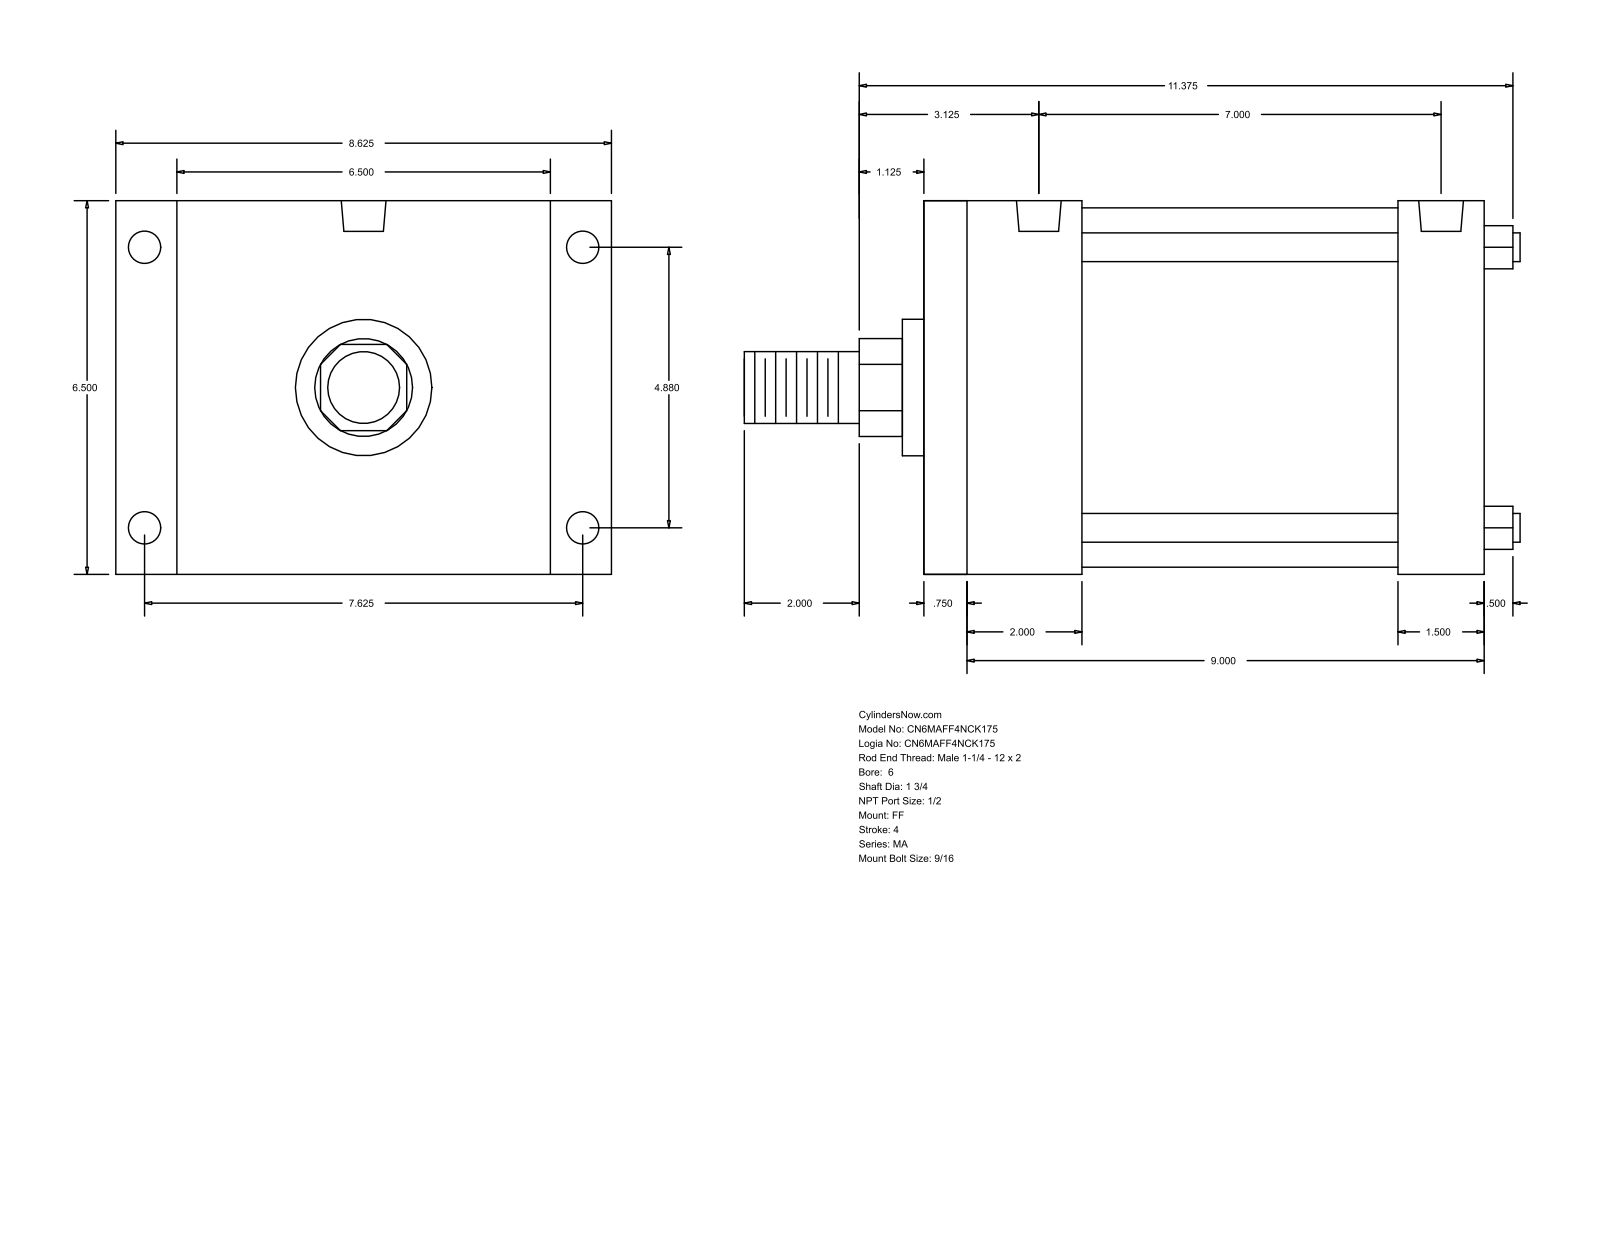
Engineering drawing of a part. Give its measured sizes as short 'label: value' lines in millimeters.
name: MA_FF__0600_1.75
written by: GSSL Pune (CONFIG_CONTROL_DESIGN)
unit: mm
bodies: 0 solids, 92 faces (64 planar, 28 cylindrical, 0 other)
size: 342.9 × 219.07 × 165.1
holes: 4× ⌀14.29, 4× ⌀17.46, 2× ⌀19.77
bosses: 4× ⌀12.7, 1× ⌀158.75, 1× ⌀60.33, 1× ⌀44.45, 1× ⌀31.75
rounds: 1× R21.63
face distances: 165.1, 247.66, 19.05, 228.61, 69.85, 50.8, 177.81, 209.55, 190.5, 139.7
hole spacings: 123.96, 177.8, 193.68, 229.95
